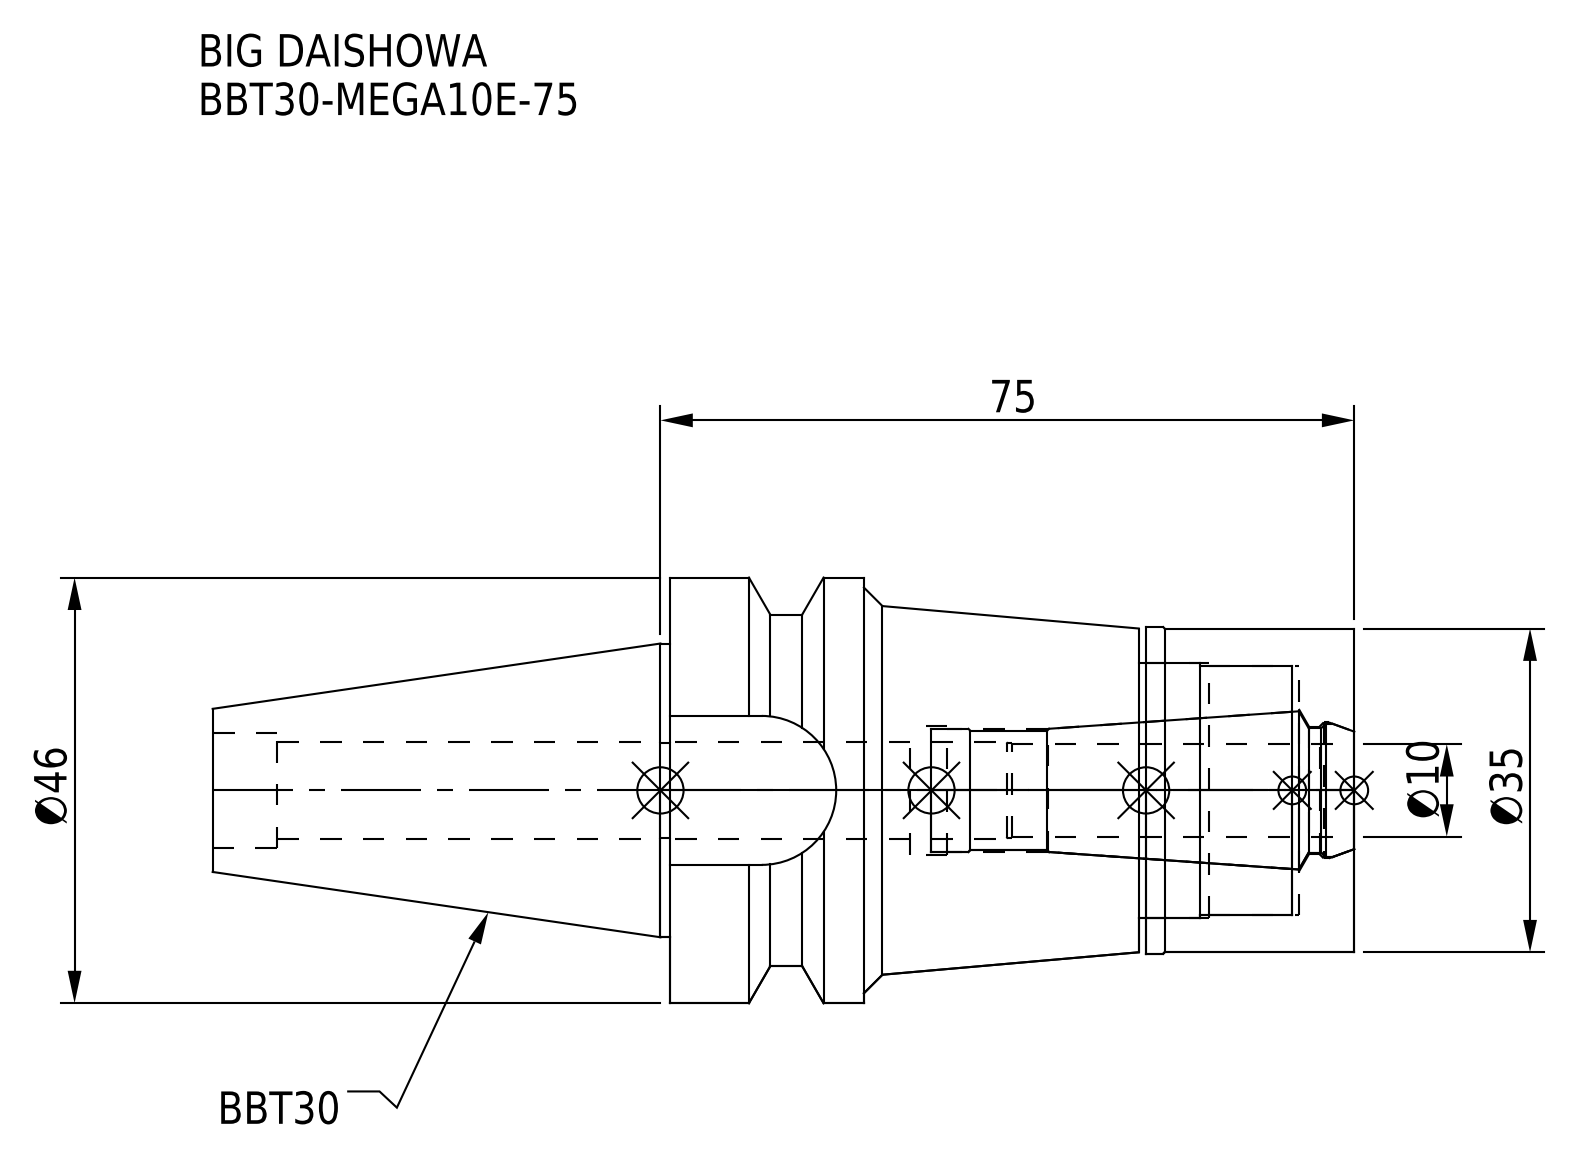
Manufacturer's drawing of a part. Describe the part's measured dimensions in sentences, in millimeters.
The part is named "BBT30-MEGA10E-75-100.stp; BBT30ME10075-100_ASM.stp; MEN10_1.stp; DXF_TEMP_ASSY_ASM_4_ASM.stp (+3 more)". Its 3-D file was written by "SolidWorks 2019 (CONFIG_CONTROL_DESIGN)". It is 2 solids with 79 faces: 21 planar, 38 cylindrical and 20 other. Overall it measures 123.4 by 46 by 46 millimeters. Its volume is 94 297 cubic millimeters and its surface area 24 716 square millimeters. Round holes: 1 of diameter 10.2, 1 of diameter 10.4, 1 of diameter 12.5, 1 of diameter 13.3, 1 of diameter 13.8, 1 of diameter 13.9, 1 of diameter 14.7, 1 of diameter 27, 1 of diameter 27.5. Round bosses or shafts: 1 of diameter 46, 1 of diameter 35.3, 1 of diameter 35, 1 of diameter 31.75. Partial cylindrical surfaces (rounded edges, fillets, slot ends): 1 of radius 8.05, 1 of radius 19. The main face-to-face distances are 74, 22.5, 51.5, 23.3, 0.8, 50.7, 6.7, 15.8, 16.6, 67.3.
